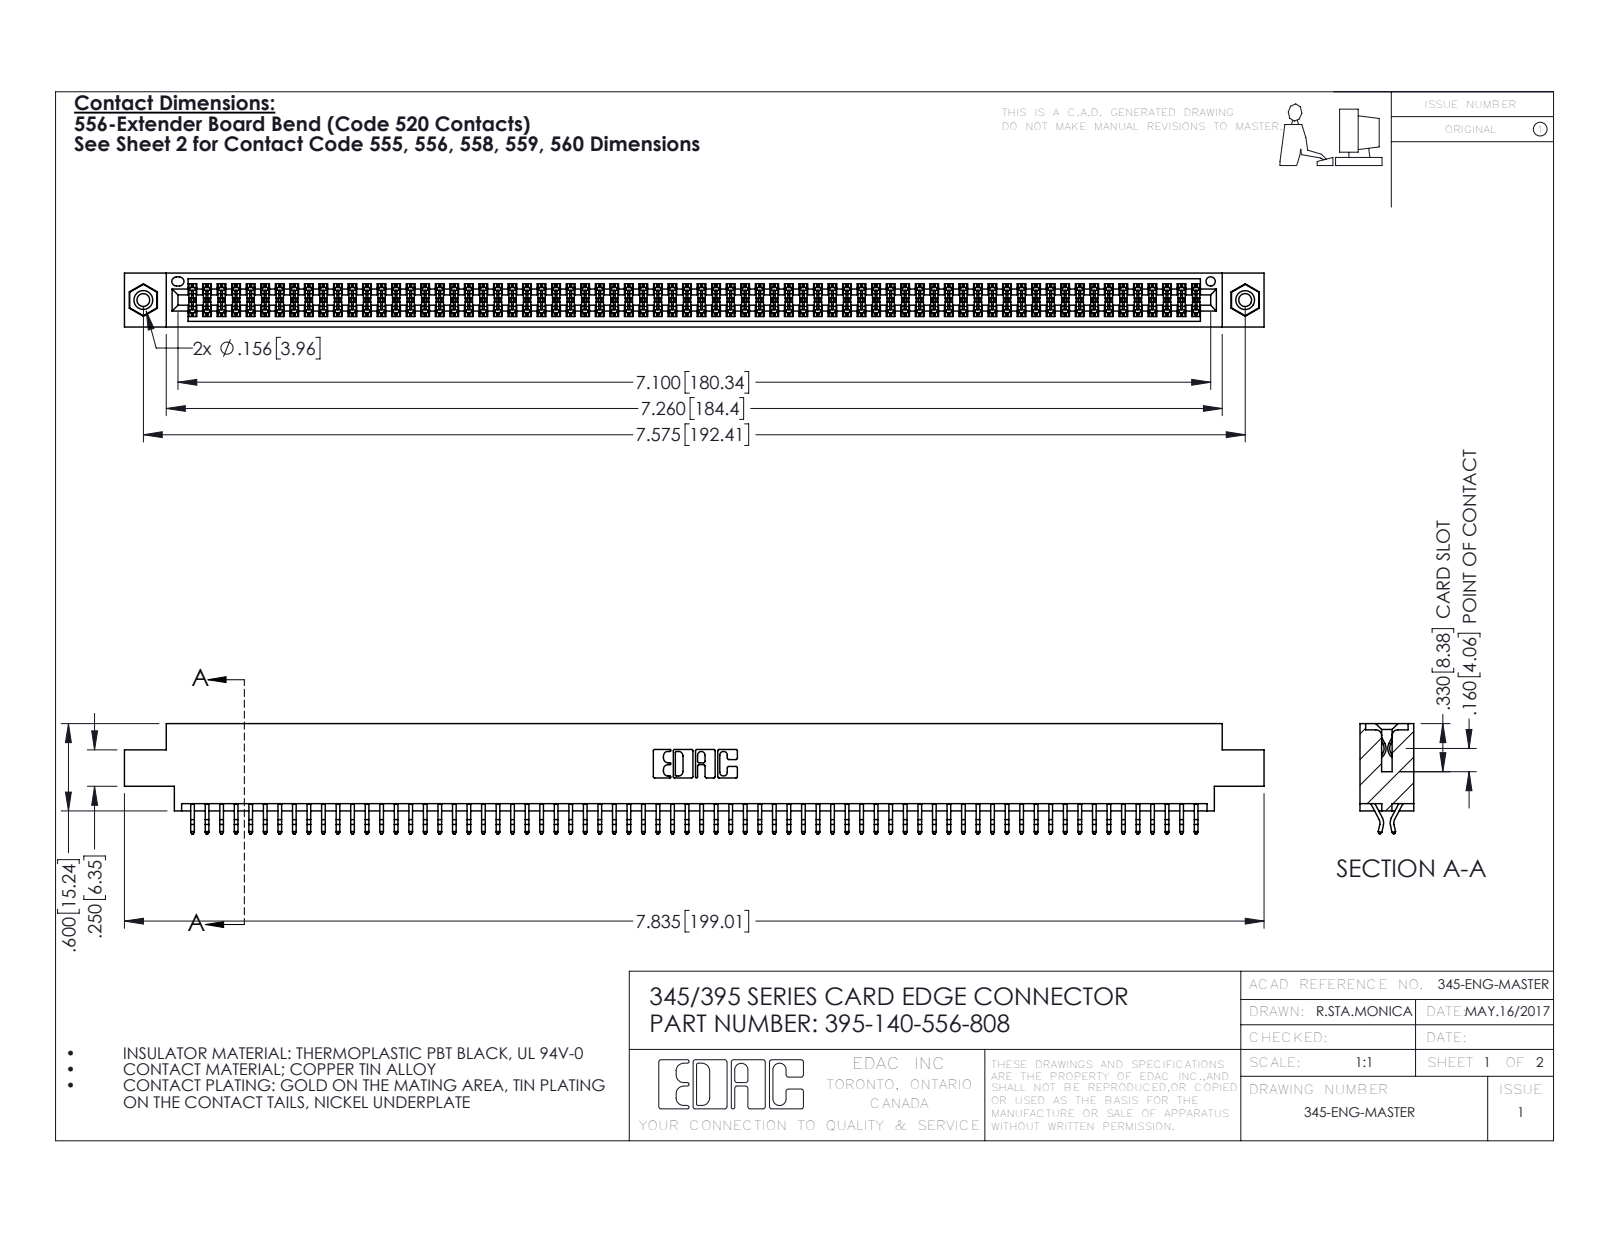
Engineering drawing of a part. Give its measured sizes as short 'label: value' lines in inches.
name: 395-140-556-808; 345-292-001_556 Tail; 345 Part_0.170 Offset - 0.156 Dia-TI; 345-250-001_345-250-003-102
written by: SolidWorks 2016 (CONFIG_CONTROL_DESIGN)
unit: in
bodies: 143 solids, 8030 faces (5296 planar, 2718 cylindrical, 16 other)
size: 7.835 × 0.757 × 0.37
volume: 1.188 in³; area: 45.49 in²
holes: 2× ⌀0.089, 2× ⌀0.125, 2× ⌀0.156, 1× ⌀0.064
bosses: 2× ⌀0.155
rounds: 210× R0.006, 22× R0.01, 6× R0.007, 6× R0.031, 3× R0.026, 2× R0.01, 2× R0.014, 2× R0.019
face distances: 0.072, 0.298, 0.37, 0.2, 0.025, 0.098, 0.272, 0.225, 0.175, 0.149
hole spacings: 0.27, 7.339, 7.575
